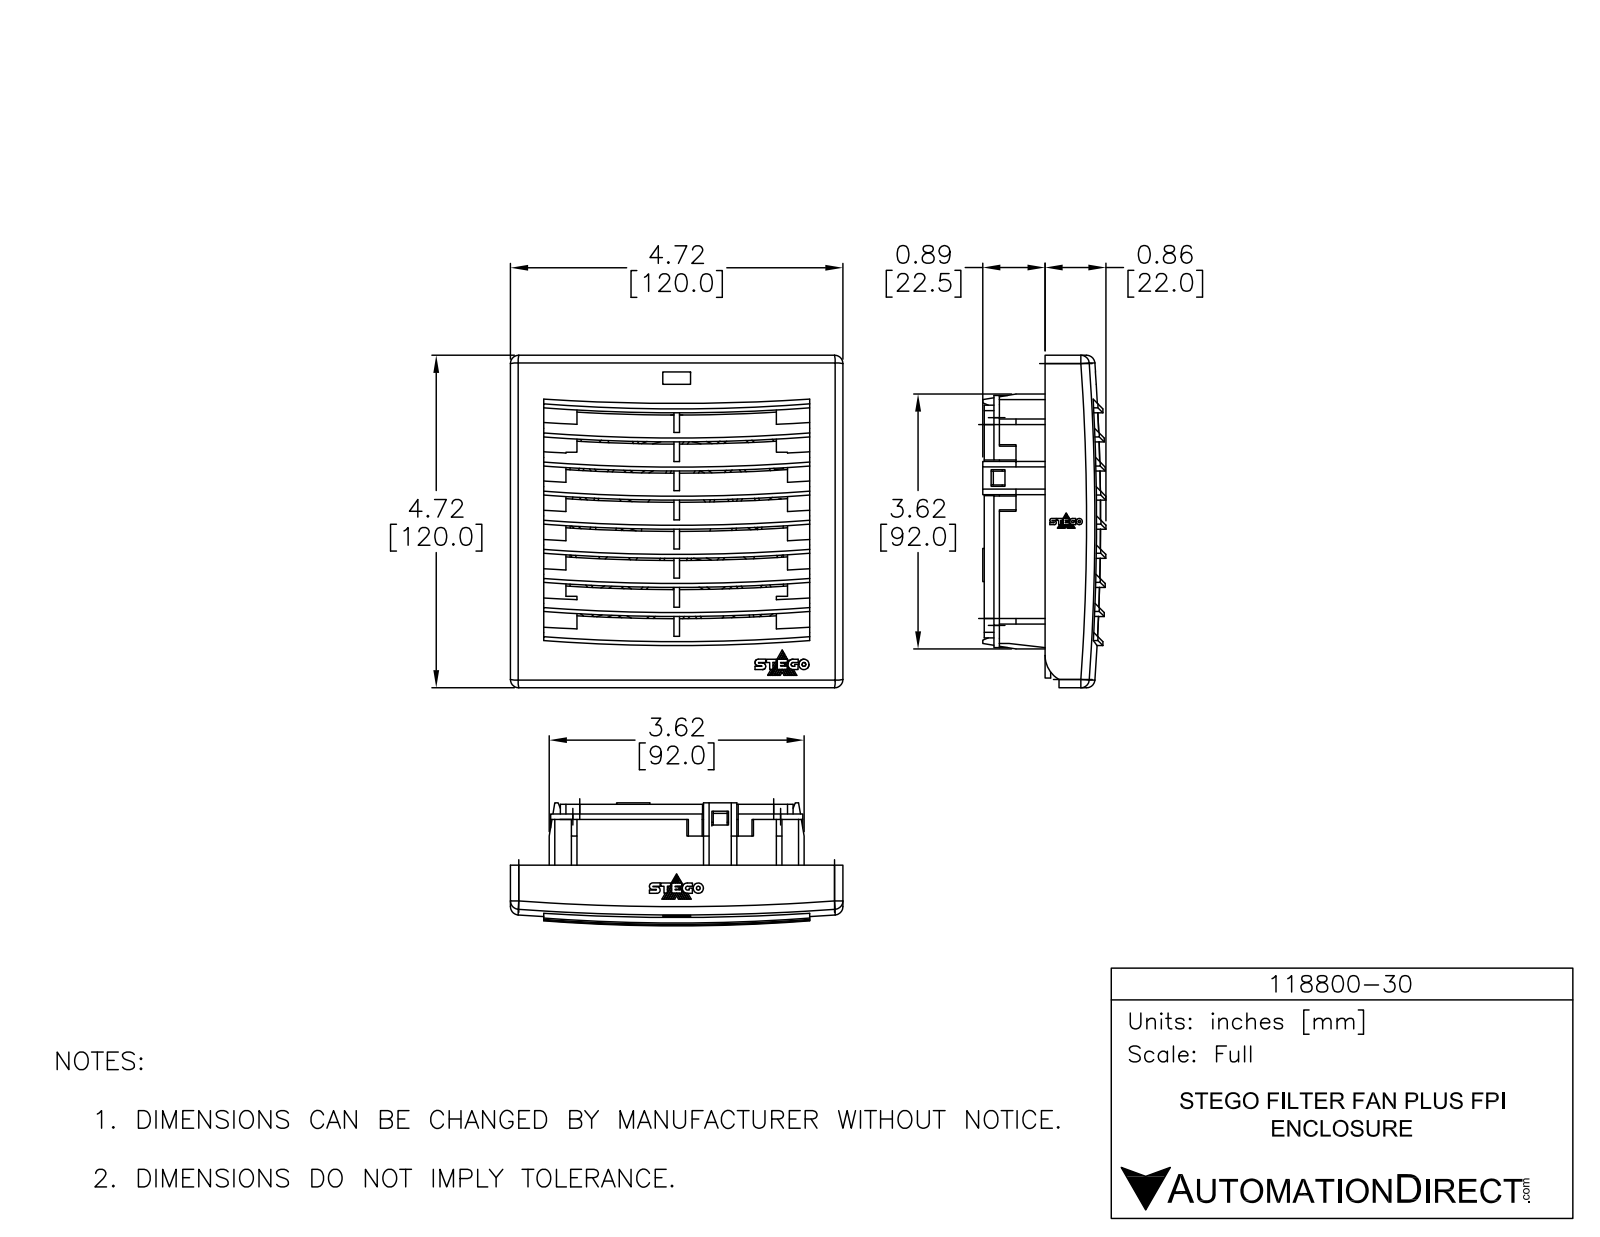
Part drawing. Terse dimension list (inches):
name: 118800-30
written by: SolidWorks 2018 (AUTOMOTIVE_DESIGN)
unit: in
bodies: 1 solid, 319 faces (173 planar, 146 cylindrical, 0 other)
size: 4.724 × 4.724 × 1.732
volume: 13.36 in³; area: 148.1 in²
holes: 1× ⌀1.996, 1× ⌀2.496, 1× ⌀3.079
bosses: 1× ⌀2.661, 1× ⌀2.161
rounds: 15× R8.63, 4× R0.118, 1× R0.539, 1× R0.748, 1× R0.83, 1× R8.226
face distances: 0.316, 0.059, 0.632, 0.375, 0.642, 4.083, 0.257, 0.26, 0.091, 3.531
